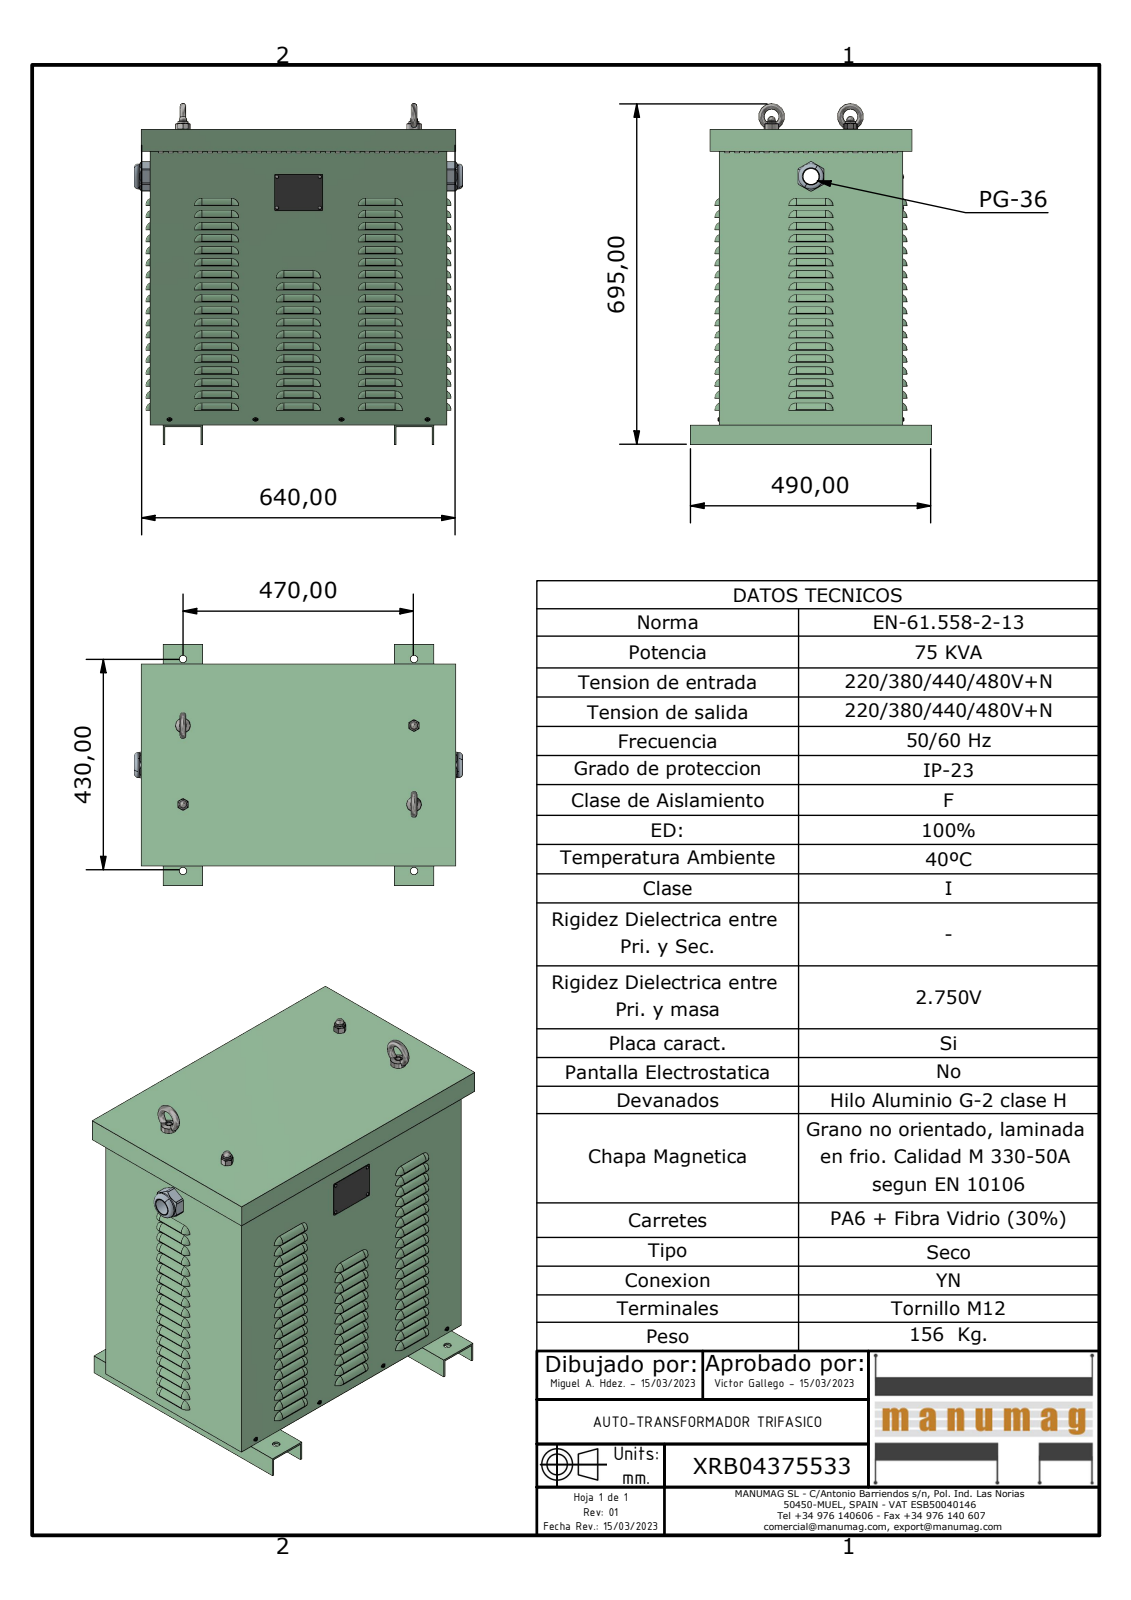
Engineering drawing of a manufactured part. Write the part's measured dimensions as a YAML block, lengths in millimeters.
part_name: "XRB04375533; JE060 - JE075 CUERPO; JE060 - JE075 BASE; JE060 - JE075 PATAS (+7 more)"
step_written_by: "Autodesk Inventor 2023 (AUTOMOTIVE_DESIGN)"
units: millimeters
bodies: {solids: 24, faces: 2907, planar: 1145, cylindrical: 1024, other: 738}
overall_size: [695, 668.2, 490]
volume: 4615000
surface_area: 4047000
round_holes:
  - {diameter: 11, count: 364}
  - {diameter: 15, count: 8}
  - {diameter: 4, count: 4}
  - {diameter: 5, count: 4}
  - {diameter: 10.11, count: 2}
  - {diameter: 11.84, count: 2}
  - {diameter: 32, count: 1}
  - {diameter: 48, count: 1}
round_bosses_or_shafts:
  - {diameter: 4, count: 4}
  - {diameter: 3.62, count: 4}
  - {diameter: 3.2, count: 4}
  - {diameter: 51.1, count: 2}
  - {diameter: 30, count: 2}
  - {diameter: 21, count: 2}
  - {diameter: 15.6, count: 2}
  - {diameter: 47.45, count: 1}
partial_cylinders:
  - {radius: 14, count: 132}
  - {radius: 7, count: 72}
  - {radius: 15, count: 72}
  - {radius: 3.88, count: 12}
  - {radius: 2.5, count: 8}
  - {radius: 2, count: 4}
  - {radius: 7.5, count: 4}
  - {radius: 30, count: 2}
face_to_face_distances: [2, 370, 600, 601, 368, 372, 602, 599, 598, 603]
hole_center_spacings: [30, 21.21, 128.88, 132, 147, 173.76, 279, 117]
